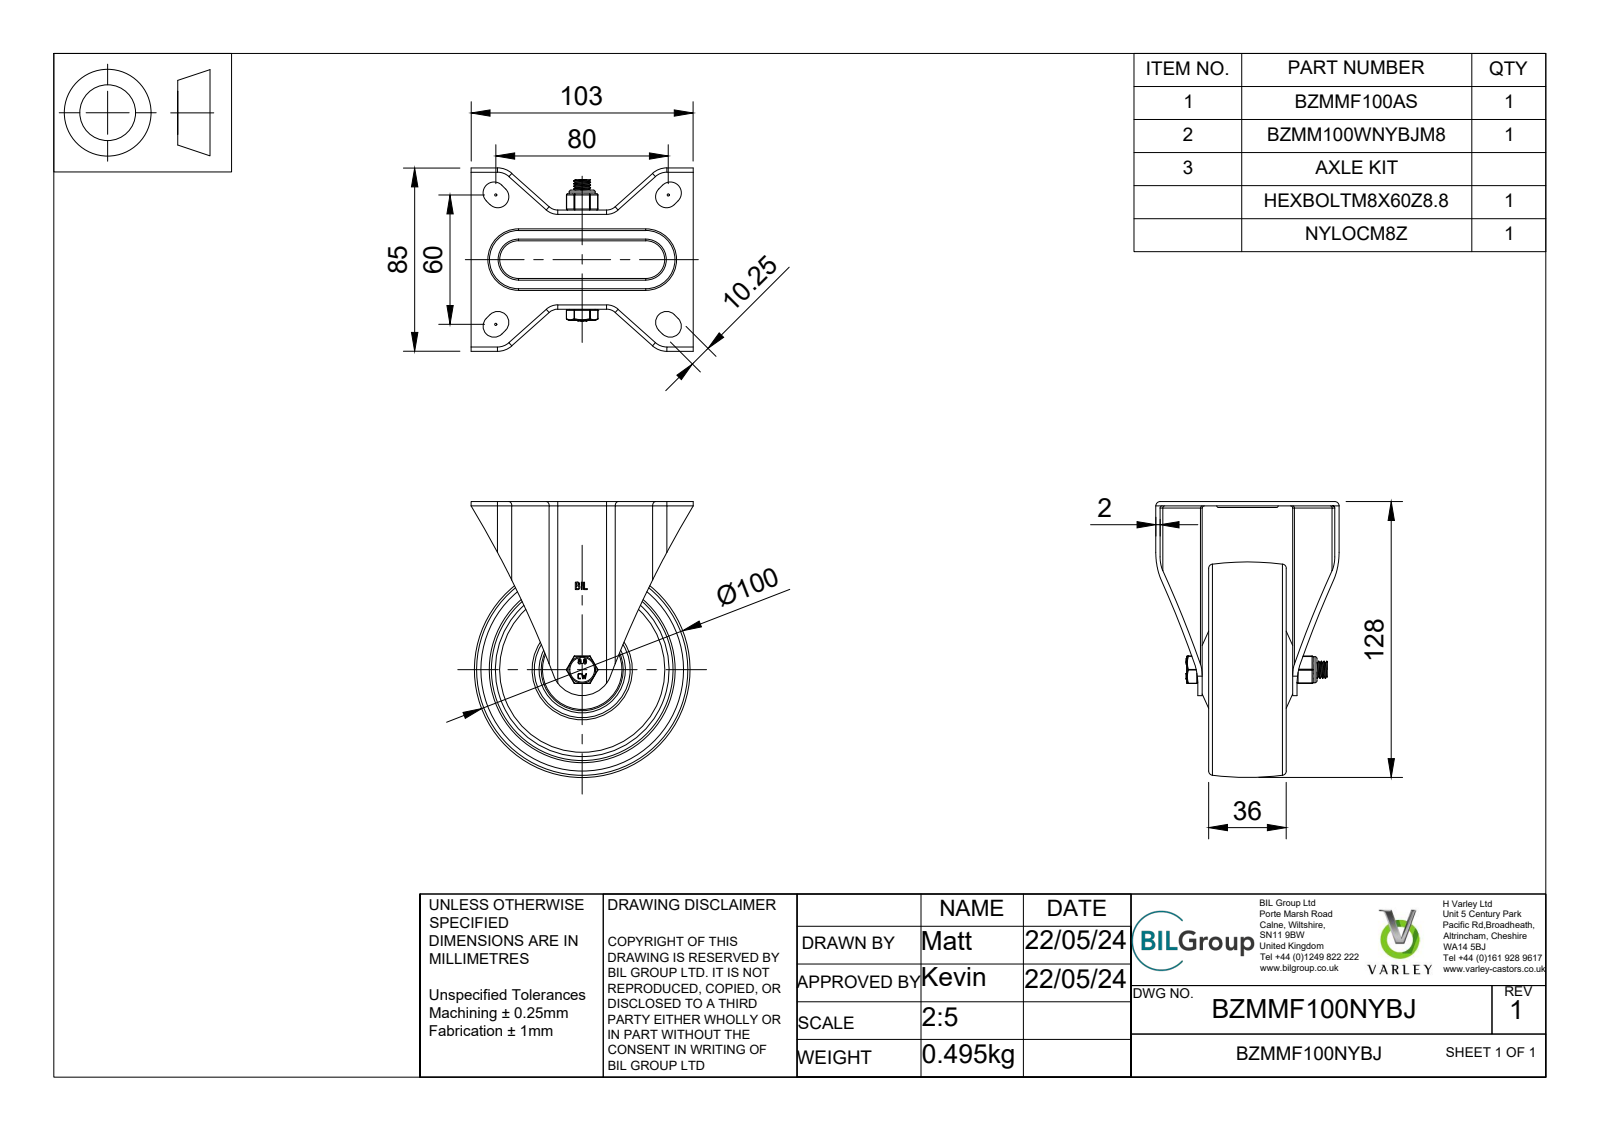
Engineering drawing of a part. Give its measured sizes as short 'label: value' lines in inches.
name: BZMMF100NYBJ v4; BZMMF100AS - 42 v1; ZINC PLATED, PRESSED STEEL BRACKET; BZMM100WNYBJM8 v1 (+7 more)
written by: Autodesk Translation Framework v13.14.0.145 (AUTOMOTIVE_DESIGN)
unit: in
bodies: 20 solids, 779 faces (278 planar, 218 cylindrical, 283 other)
size: 5.039 × 4.055 × 3.346
volume: 11.7 in³; area: 154.2 in²
holes: 2× ⌀0.026, 1× ⌀0.315, 1× ⌀0.323, 1× ⌀0.325, 1× ⌀0.339, 1× ⌀0.591, 1× ⌀0.787, 1× ⌀0.886, 1× ⌀0.984, 1× ⌀1.181, 1× ⌀1.22, 1× ⌀1.26
bosses: 1× ⌀1.752, 1× ⌀1.496, 1× ⌀1.201, 1× ⌀1.102, 1× ⌀0.906, 1× ⌀0.748, 1× ⌀0.709, 1× ⌀0.587
rounds: 18× R0.02, 12× R0.01, 8× R0.03, 8× R0.039, 8× R0.079, 8× R0.202, 4× R0.013, 4× R0.025
face distances: 0.079, 0.679, 0.974, 0.561, 1.053, 0.758, 1.732, 0.295, 0.03, 0.197
hole spacings: 0.183, 0.098
